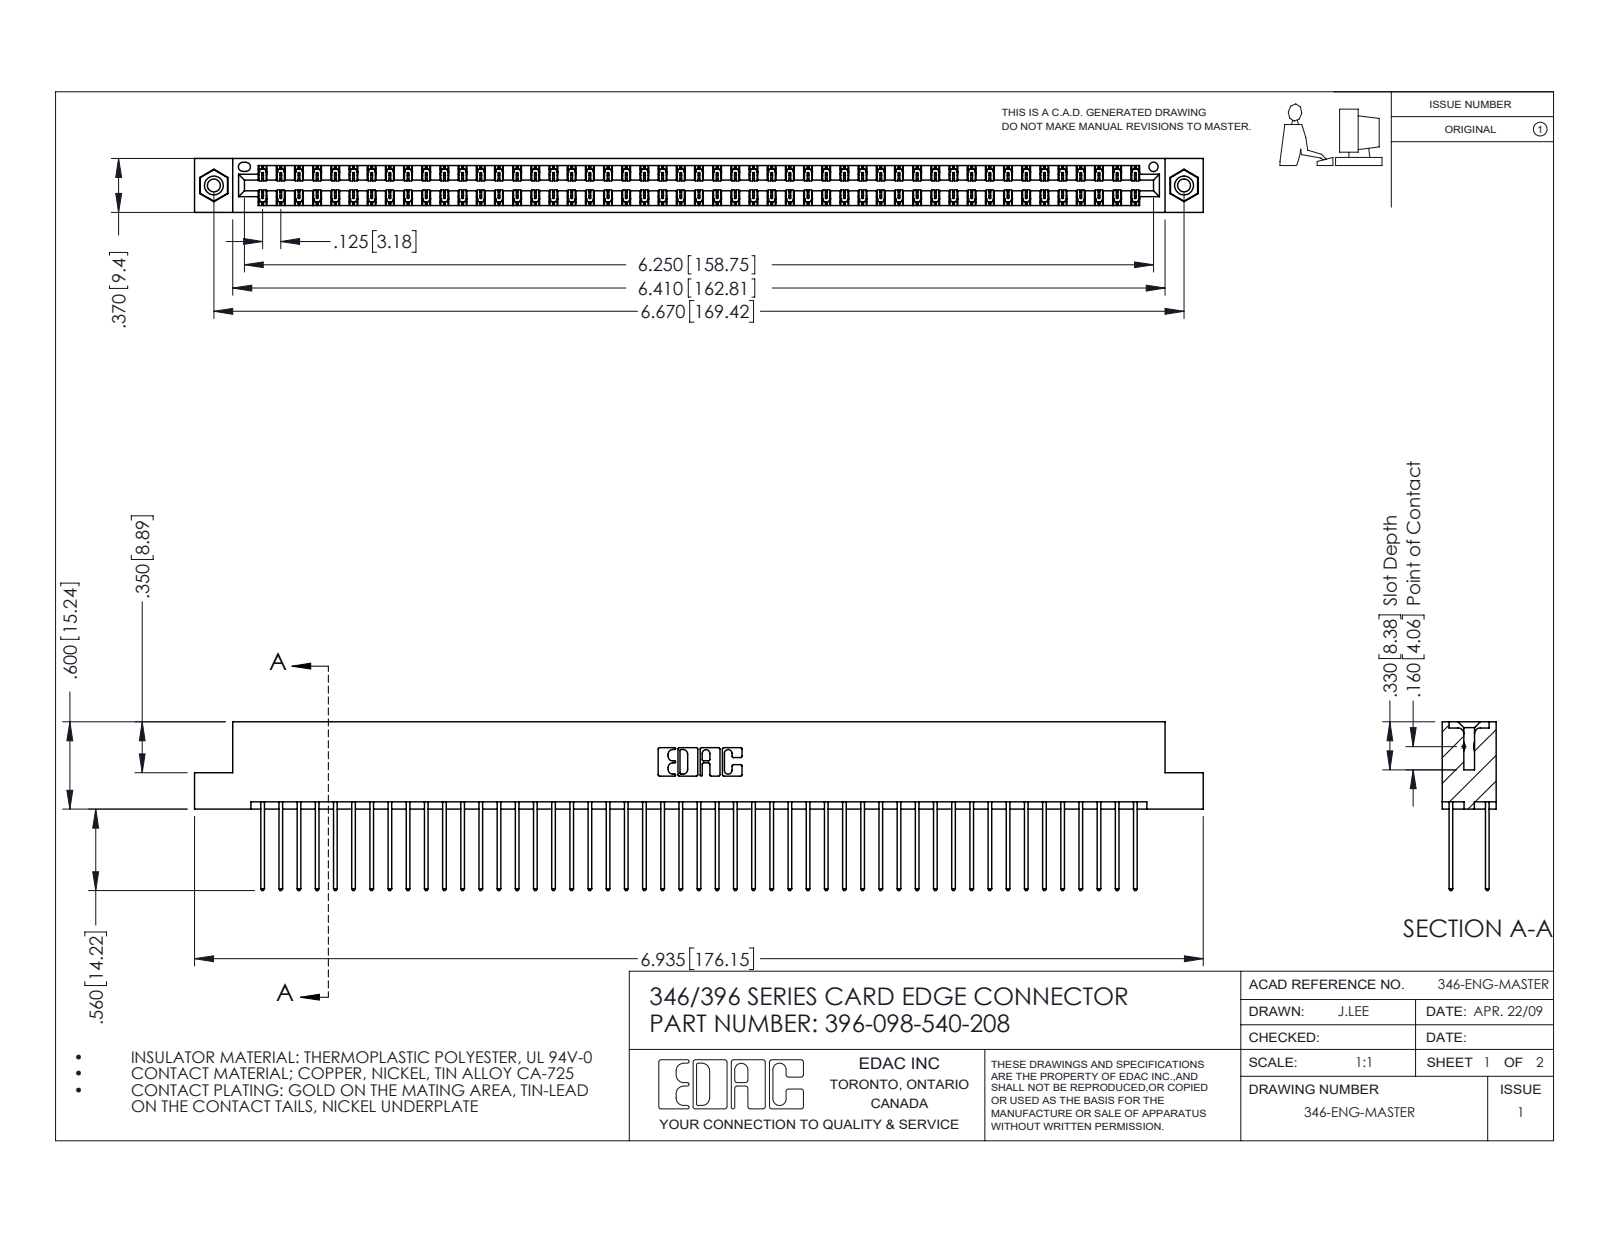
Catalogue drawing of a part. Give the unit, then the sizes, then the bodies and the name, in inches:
Units: inches
Overall size (bounding box): 6.935 × 1.16 × 0.37
Round holes (diameter × count): ⌀0.089 ×2, ⌀0.125 ×2, ⌀0.156 ×2, ⌀0.064 ×1
Round bosses / shafts (diameter × count): ⌀0.155 ×2
Partial cylindrical surfaces — rounded edges, fillets, slot ends (radius × count): R0.006 ×147, R0.01 ×98, R0.01 ×22, R0.007 ×6, R0.031 ×6, R0.026 ×3, R0.014 ×2, R0.022 ×2
Main face-to-face distances: 0.048, 0.322, 0.25, 0.072, 0.298, 0.025, 0.37, 0.275, 0.148, 0.222
Hole centre spacings: 0.246, 6.461, 6.67
Volume: 1.074 in³ · Surface area: 40.42 in²
Bodies: 101 solids, 5278 faces (3538 planar, 1724 cylindrical, 16 other)
Part name (STEP PRODUCT): 396-098-540-208; 345-250-001_345-250-003-102; 345-292-001_345-293-140; 346 Part_Flush Mounting Lugs - 0.156 Dia-TI
STEP written by: SolidWorks 2016 (CONFIG_CONTROL_DESIGN)
